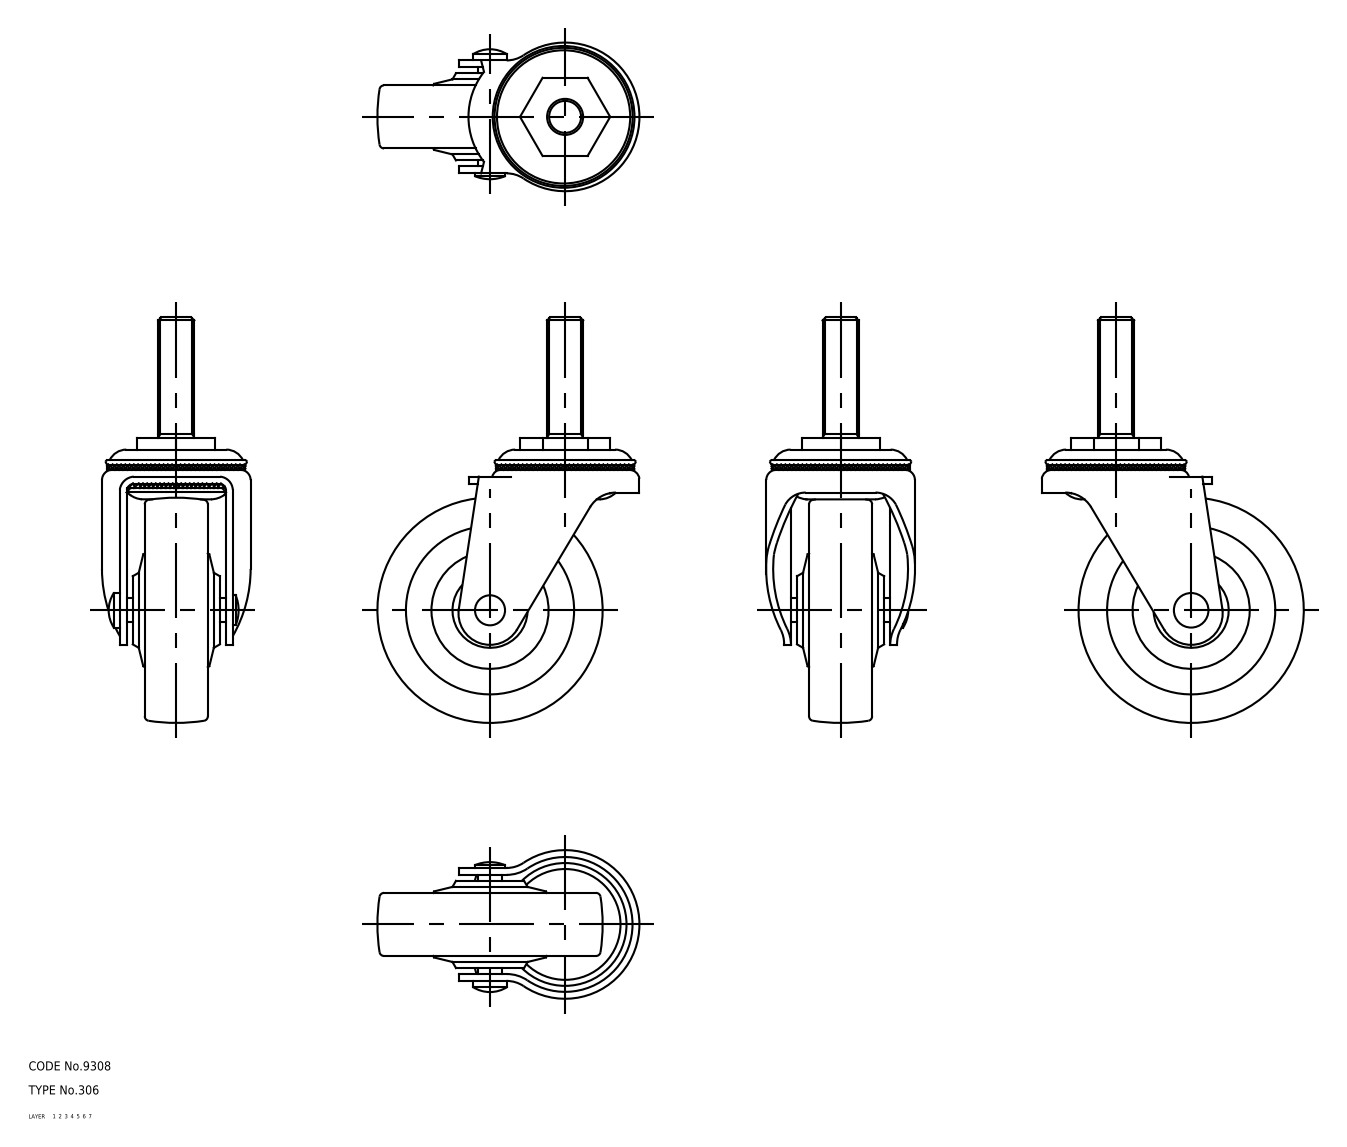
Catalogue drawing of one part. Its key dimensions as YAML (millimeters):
part_name: "67119161; 67119174; 67119187; 67119200"
step_written_by: "CADfix (AUTOMOTIVE_DESIGN)"
units: millimeters
bodies: {solids: 4, faces: 153, planar: 0, cylindrical: 0, other: 153}
overall_size: [135.1, 87.25, 49.5]
volume: 132868
surface_area: 33218
